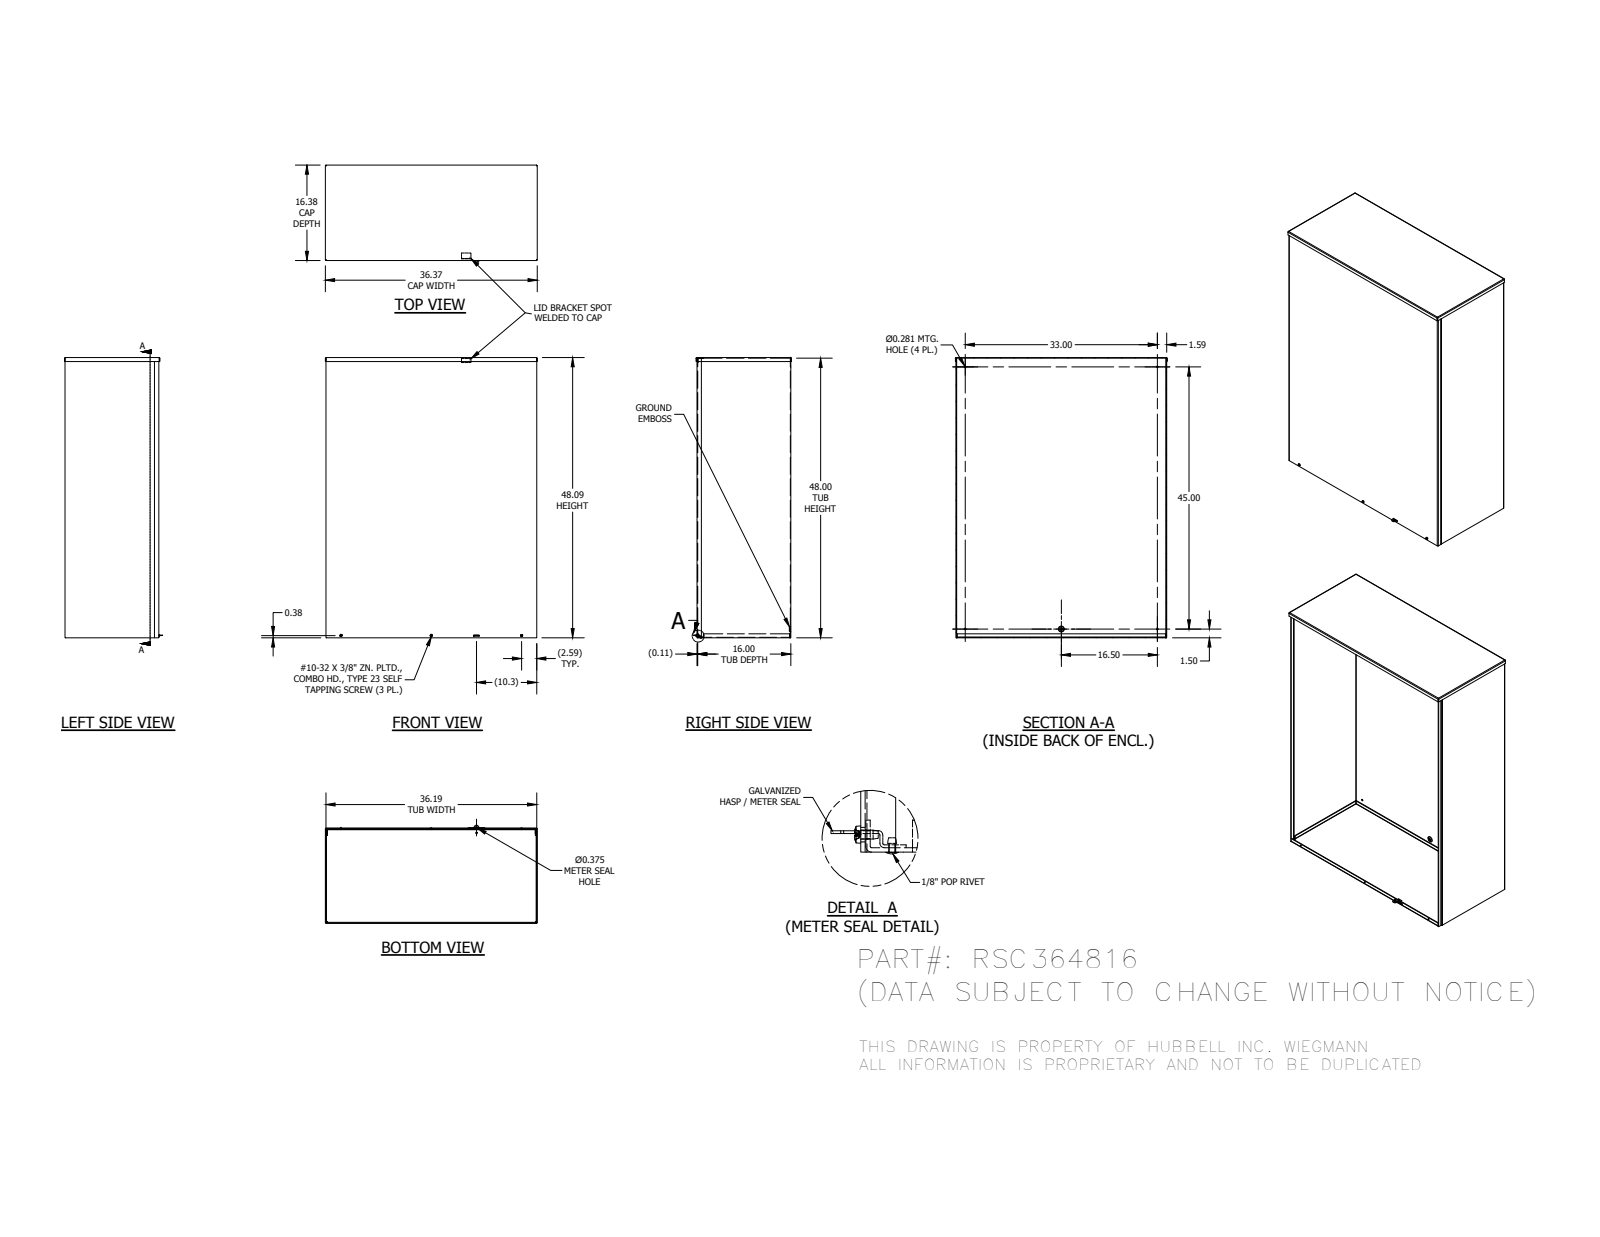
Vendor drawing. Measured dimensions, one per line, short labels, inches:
name: RSC364816BKPA; RSC3616EWPA; RSC3648LFA; RSC3616CPA (+5 more)
written by: Autodesk Inventor 2014 (AUTOMOTIVE_DESIGN)
unit: in
bodies: 11 solids, 367 faces (226 planar, 64 cylindrical, 77 other)
size: 48.134 × 36.375 × 16.844
volume: 594.9 in³; area: 12 760 in²
holes: 6× ⌀0.313, 4× ⌀0.171, 4× ⌀0.281, 1× ⌀0.125, 1× ⌀0.136, 1× ⌀0.375
bosses: 3× ⌀0.19, 1× ⌀0.262, 1× ⌀0.125
rounds: 19× R0.031, 16× R0.125, 2× R0.093, 1× R0.105, 1× R0.4
face distances: 0.094, 16.016, 16.109, 15.922, 36.094, 48, 36.187, 36, 48.094, 47.906
hole spacings: 15.5, 32.02, 49.728, 16.538, 48.987, 1.506, 15.541, 31
